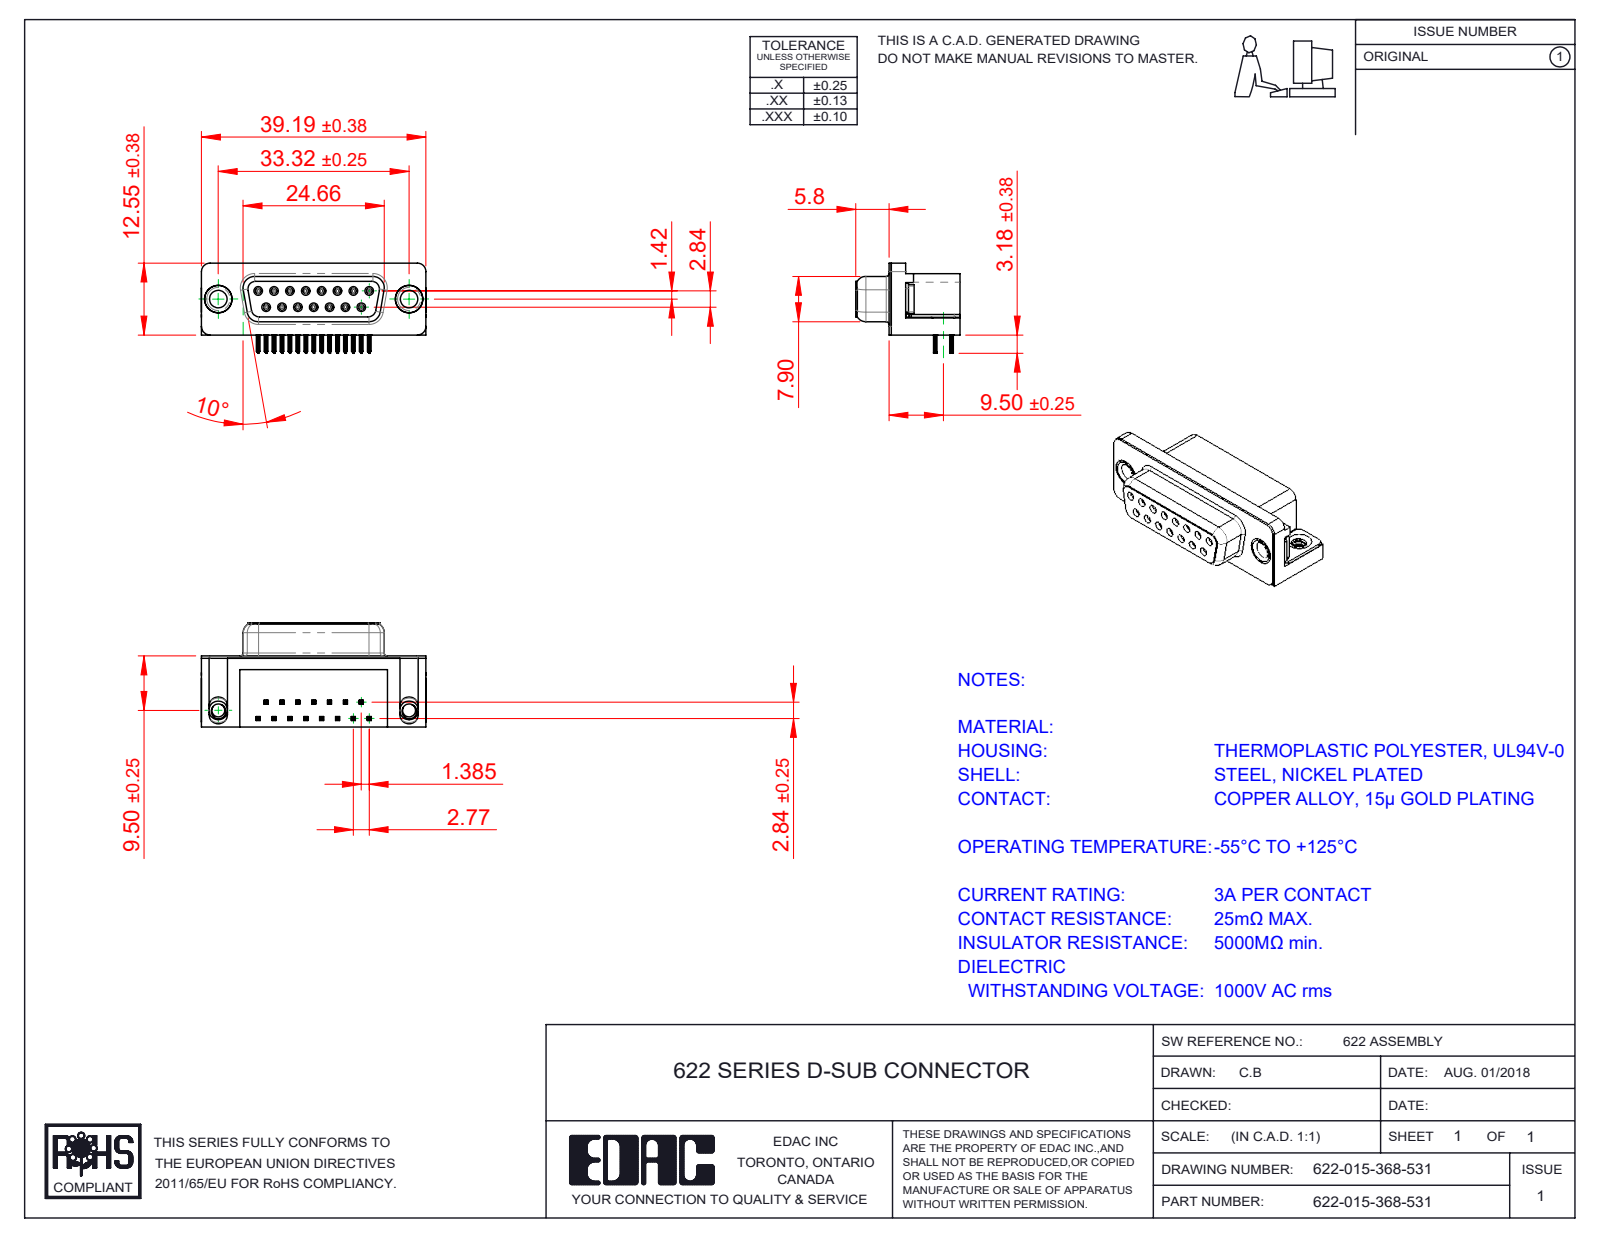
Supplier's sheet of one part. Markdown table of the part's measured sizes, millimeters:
| quantity | value |
| --- | --- |
| part name | 622-015-368-531; 622 Contact Top; 622 Shell_15 Socket; 622 Housing_15 Socket (+3 more) |
| STEP written by | SolidWorks 2016 (CONFIG_CONTROL_DESIGN) |
| units | millimeters |
| bodies | 21 solids, 2427 faces (1106 planar, 595 cylindrical, 726 other) |
| overall size | 39.22 × 18.2 × 16.25 |
| volume | 5 175 mm³ |
| surface area | 6 698 mm² |
| round holes (diameter × count) | 0.8 × 15, 0.9 × 15, 3.05 × 2, 4 × 2, 4.8 × 2, 5 × 2 |
| round bosses / shafts (diameter × count) | 1.2 × 15, 4.9 × 2, 4.75 × 2, 3.85 × 2 |
| partial cylindrical surfaces (radius × count) | 0.1 × 120, 0.15 × 60, 0.35 × 30, 1 × 18, 0.34 × 15, 0.5 × 10, 0.25 × 8, 1.35 × 8 |
| main face-to-face distances | 0.4, 12, 6.2, 12.4, 10.35, 2.9, 0.85, 6.65, 0.35, 0.5 |
| hole center spacings | 3.16, 2.77, 5.54, 8.31, 11.08, 5.03, 5.04, 7.48 |
